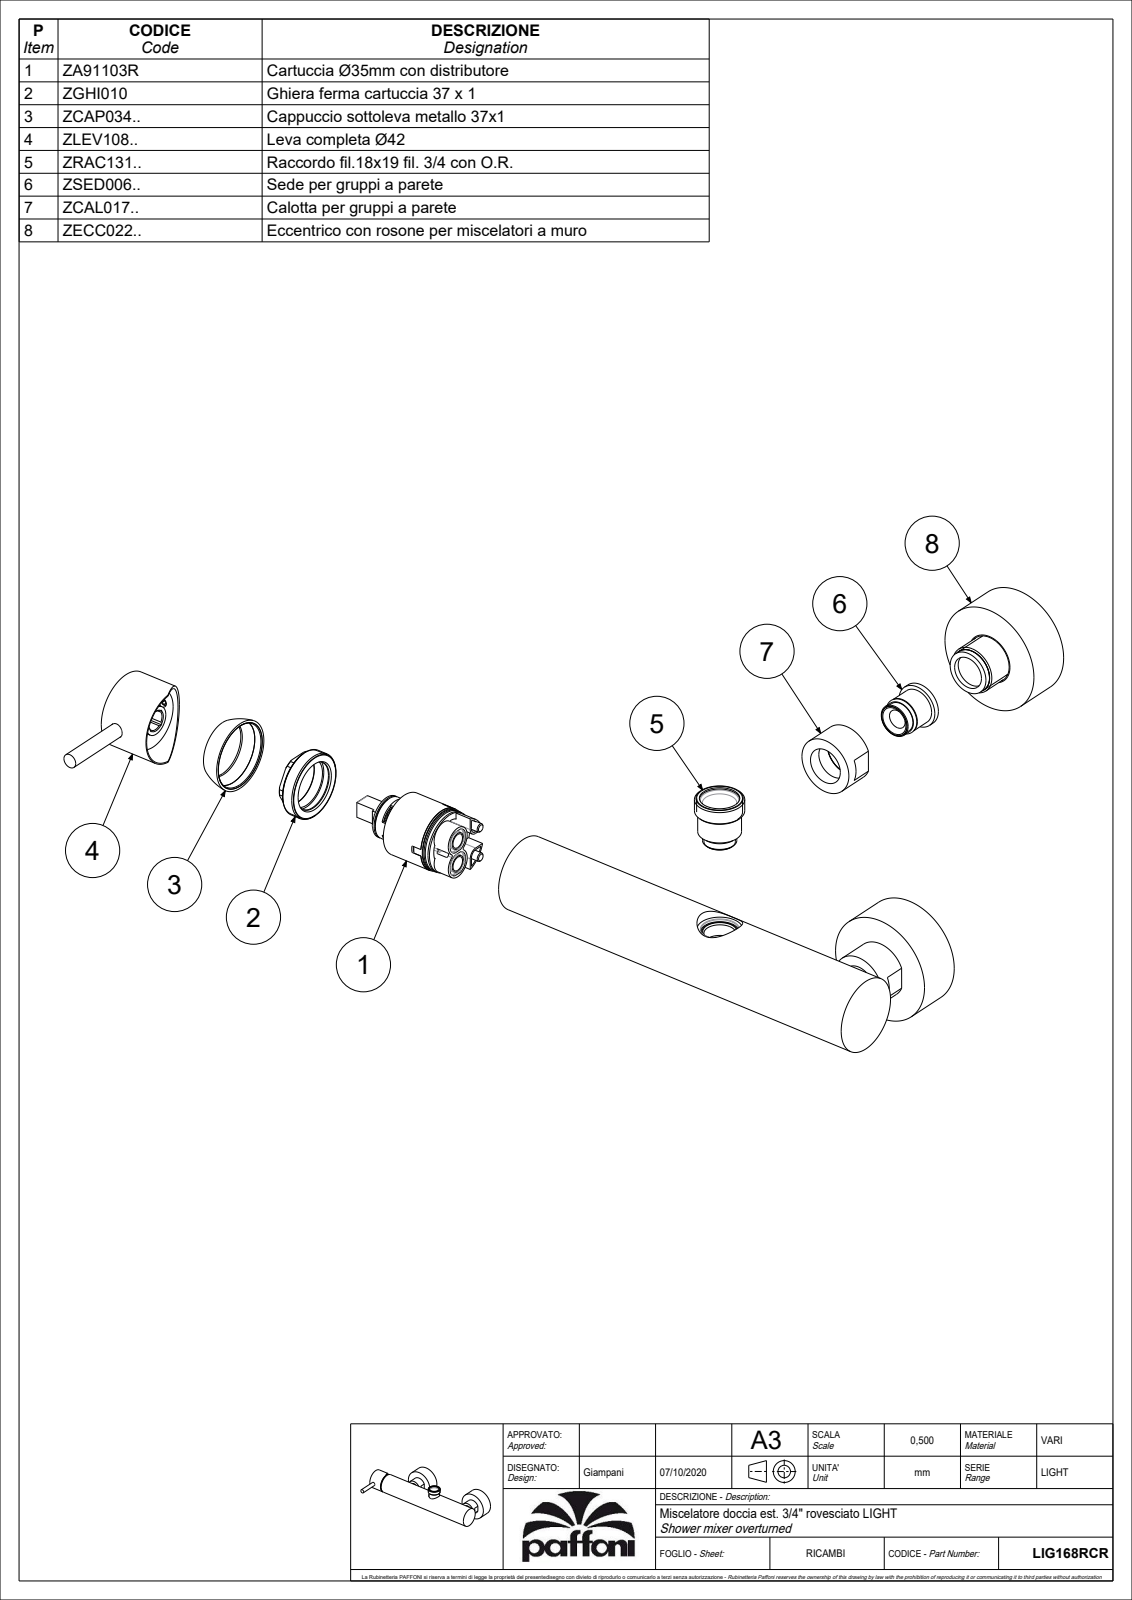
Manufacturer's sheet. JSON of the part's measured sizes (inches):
{"part_name": "LIG168RCR", "step_written_by": "CREO PARAMETRIC BY PTC INC, 2020044 (CONFIG_CONTROL_DESIGN)", "units": "inches", "bodies": {"solids": 0, "faces": 58, "planar": 20, "cylindrical": 24, "other": 14}, "overall_size": [10.571, 4.938, 2.602], "round_bosses_or_shafts": [[2.35, 2], [1.634, 2], [1.24, 2], [0.776, 2], [1.039, 1], [0.906, 1], [0.311, 1], [0.299, 1]], "face_to_face_distances": [0.984, 1.693, 0.709, 0.335, 1.142, 5.906, 1.673, 2.815, 7.579, 8.72]}
